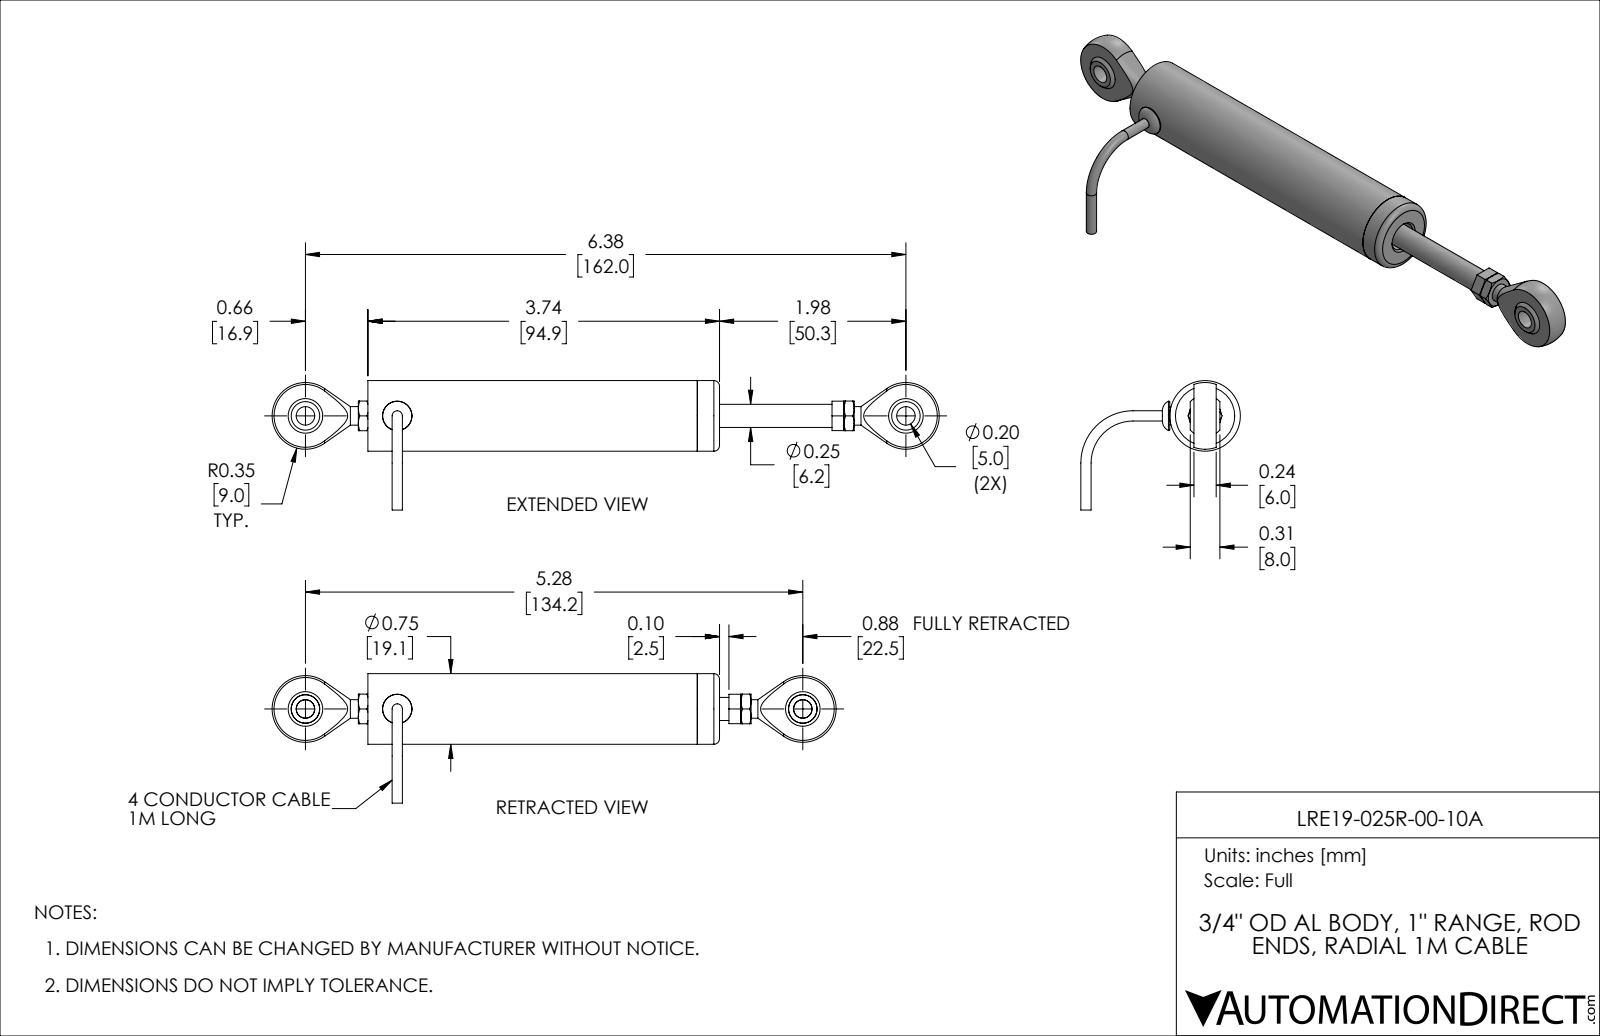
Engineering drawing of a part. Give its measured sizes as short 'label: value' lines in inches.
name: LRE19-025R-00-10A_retracted
written by: SolidWorks 2019 (AUTOMOTIVE_DESIGN)
unit: in
bodies: 13 solids, 161 faces (58 planar, 34 cylindrical, 69 other)
size: 5.993 × 1.695 × 1.375
volume: 0.927 in³; area: 29.54 in²
holes: 3× ⌀0.197, 1× ⌀0.109, 1× ⌀0.165, 1× ⌀0.188, 1× ⌀0.193, 1× ⌀0.221, 1× ⌀0.307, 1× ⌀0.62, 1× ⌀0.625, 1× ⌀0.65, 1× ⌀0.71, 1× ⌀0.725
bosses: 1× ⌀0.75, 1× ⌀0.7, 1× ⌀0.624, 1× ⌀0.246, 1× ⌀0.223, 1× ⌀0.218, 1× ⌀0.109
face distances: 0.236, 0.105, 3.626, 3.731, 3.495, 3.39, 0.236, 0.315, 0.039, 0.276
hole spacings: 0.975, 4.309, 5.284
